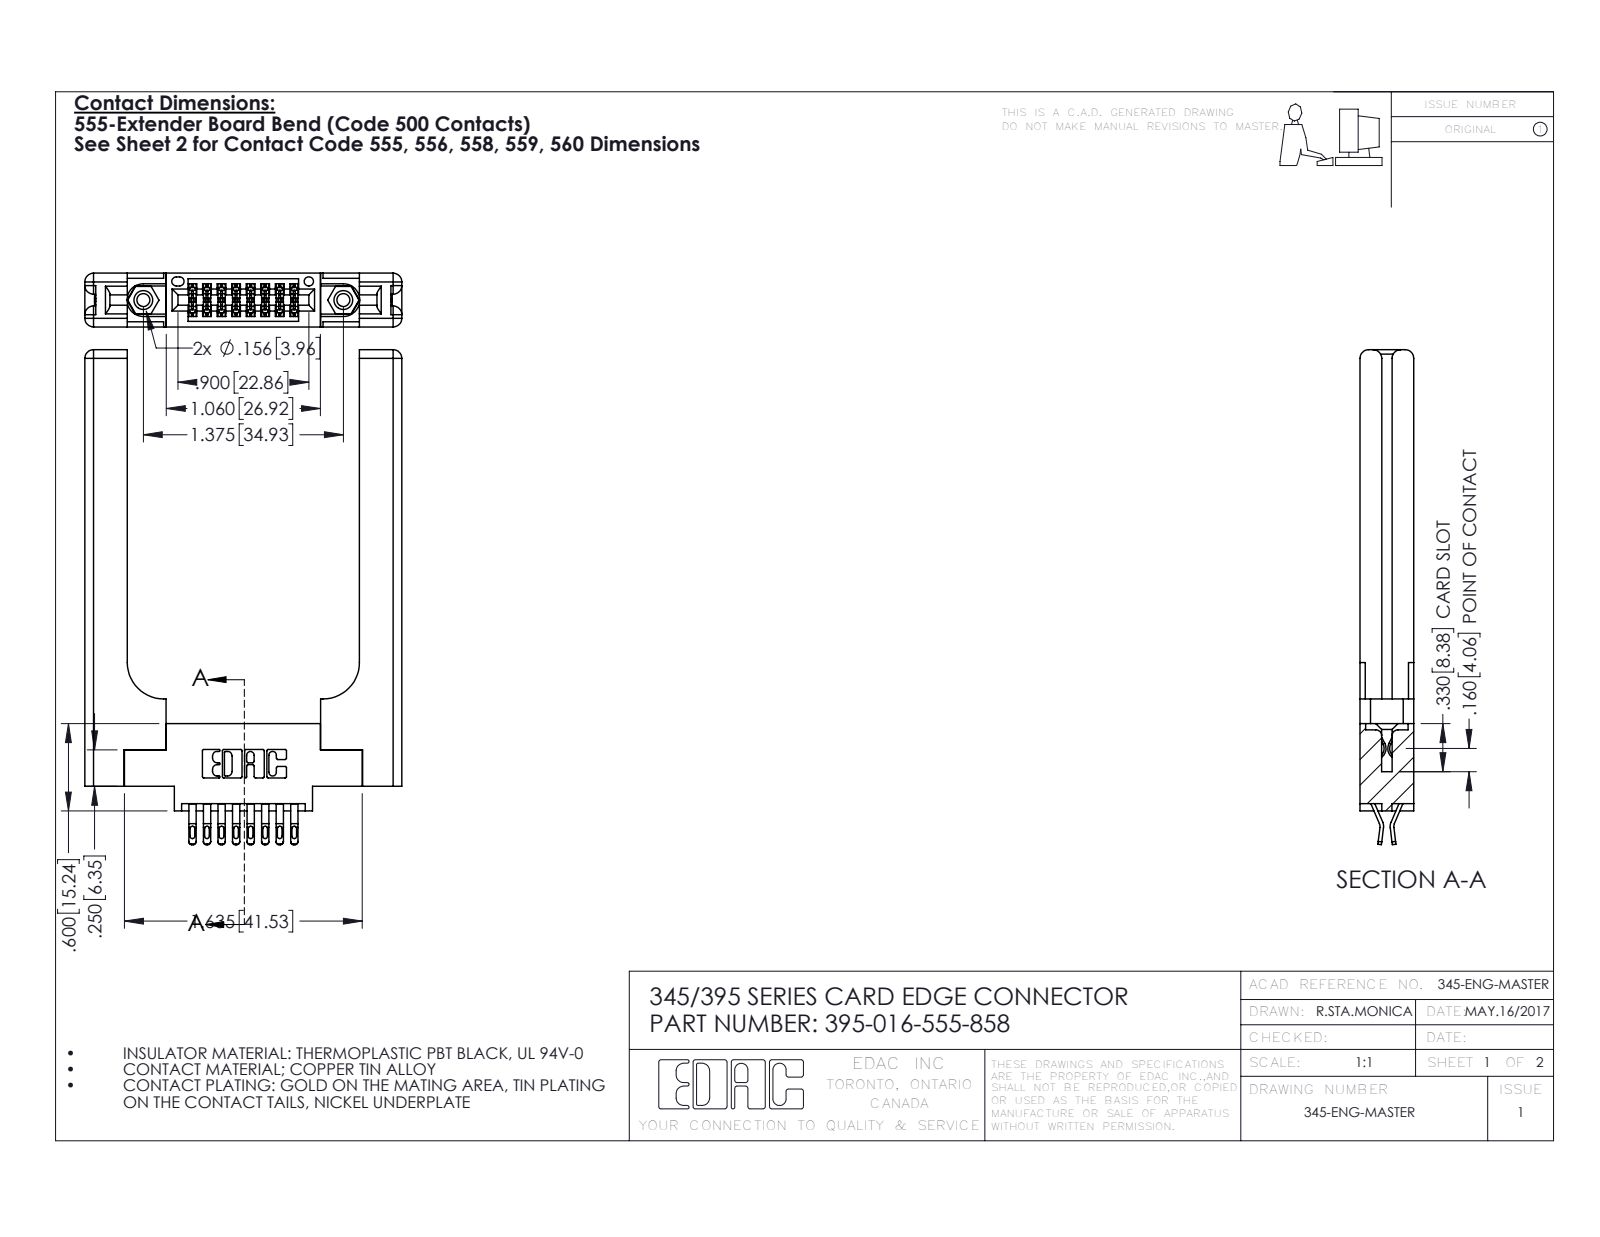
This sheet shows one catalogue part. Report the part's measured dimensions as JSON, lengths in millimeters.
{"part_name": "345-250-001_345-250-001-102; 345-292-001_555 Tail; 345-220-058_345-220-058; 395-016-555-858 (+1 more)", "step_written_by": "SolidWorks 2016 (CONFIG_CONTROL_DESIGN)", "units": "millimeters", "bodies": {"solids": 21, "faces": 1282, "planar": 728, "cylindrical": 494, "other": 60}, "overall_size": [86.4, 55.3, 9.4], "volume_mm3": 13500, "surface_area_mm2": 12080, "round_holes": [[2.3, 2], [3.2, 2], [4, 2], [1.6, 1]], "round_bosses_or_shafts": [[3.9, 2]], "partial_cylinders_radius": [[0.4, 40], [0.5, 32], [0.2, 24], [0.3, 22], [1.5, 16], [0.2, 6], [0.8, 6], [0.7, 3]], "face_to_face_distances": [9.4, 3.8, 5.6, 1.8, 3.8, 2, 7.6, 40.5, 1.8, 3], "hole_center_spacings": [6.9, 29.1, 34.9]}
